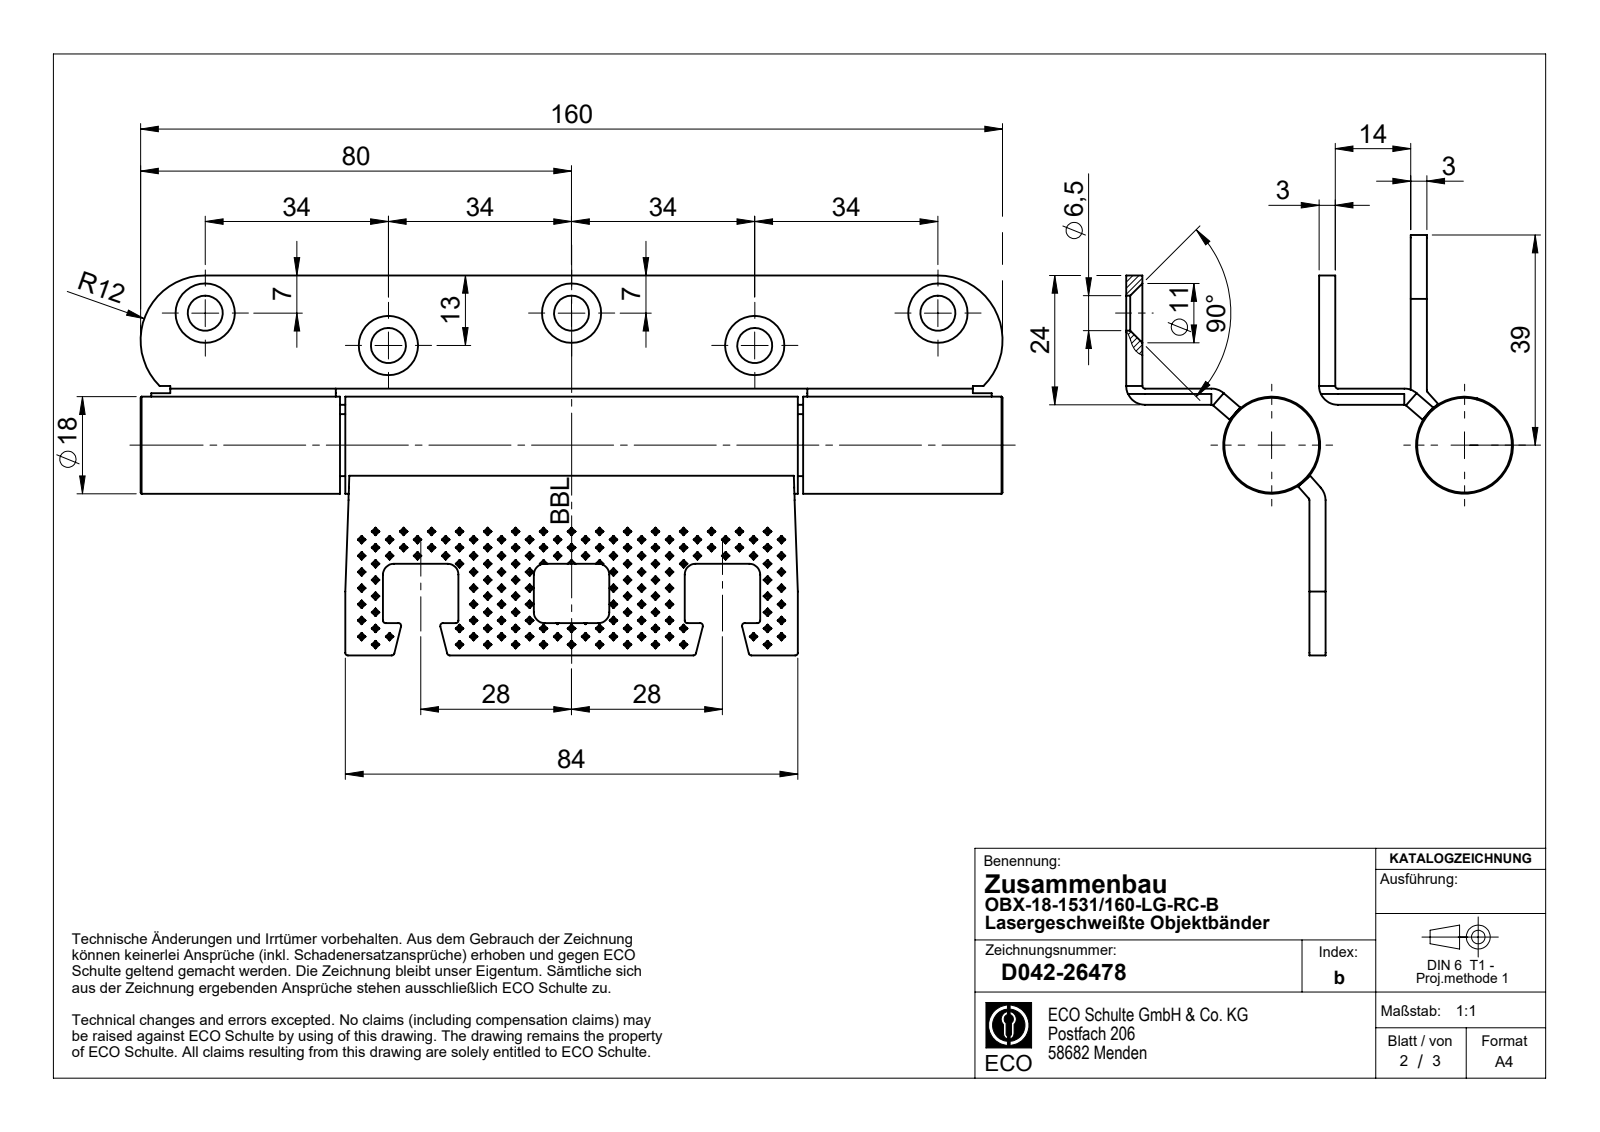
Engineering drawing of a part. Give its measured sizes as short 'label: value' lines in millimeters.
name: B01572; D044-14308; D044-14309; DIN5401-III (+4 more)
written by: SolidWorks 2020 (CONFIG_CONTROL_DESIGN)
unit: mm
bodies: 11 solids, 1722 faces (1490 planar, 135 cylindrical, 97 other)
size: 160 × 48 × 36
volume: 63 176 mm³; area: 35 053 mm²
holes: 5× ⌀6.5, 2× ⌀2, 1× ⌀0.5, 1× ⌀4.5, 1× ⌀7.9
bosses: 1× ⌀18, 1× ⌀12, 1× ⌀11.8, 1× ⌀11.5, 1× ⌀7.7, 1× ⌀4, 1× ⌀1.65
rounds: 17× R0.5, 8× R2, 6× R0.25, 3× R3.5, 2× R0.68, 2× R2.1, 2× R3, 2× R12
face distances: 3, 17, 14, 20, 21, 11.5, 122, 24, 38, 148.5
hole spacings: 34.53, 68, 102.18, 1.95, 4.25, 4.6, 136
